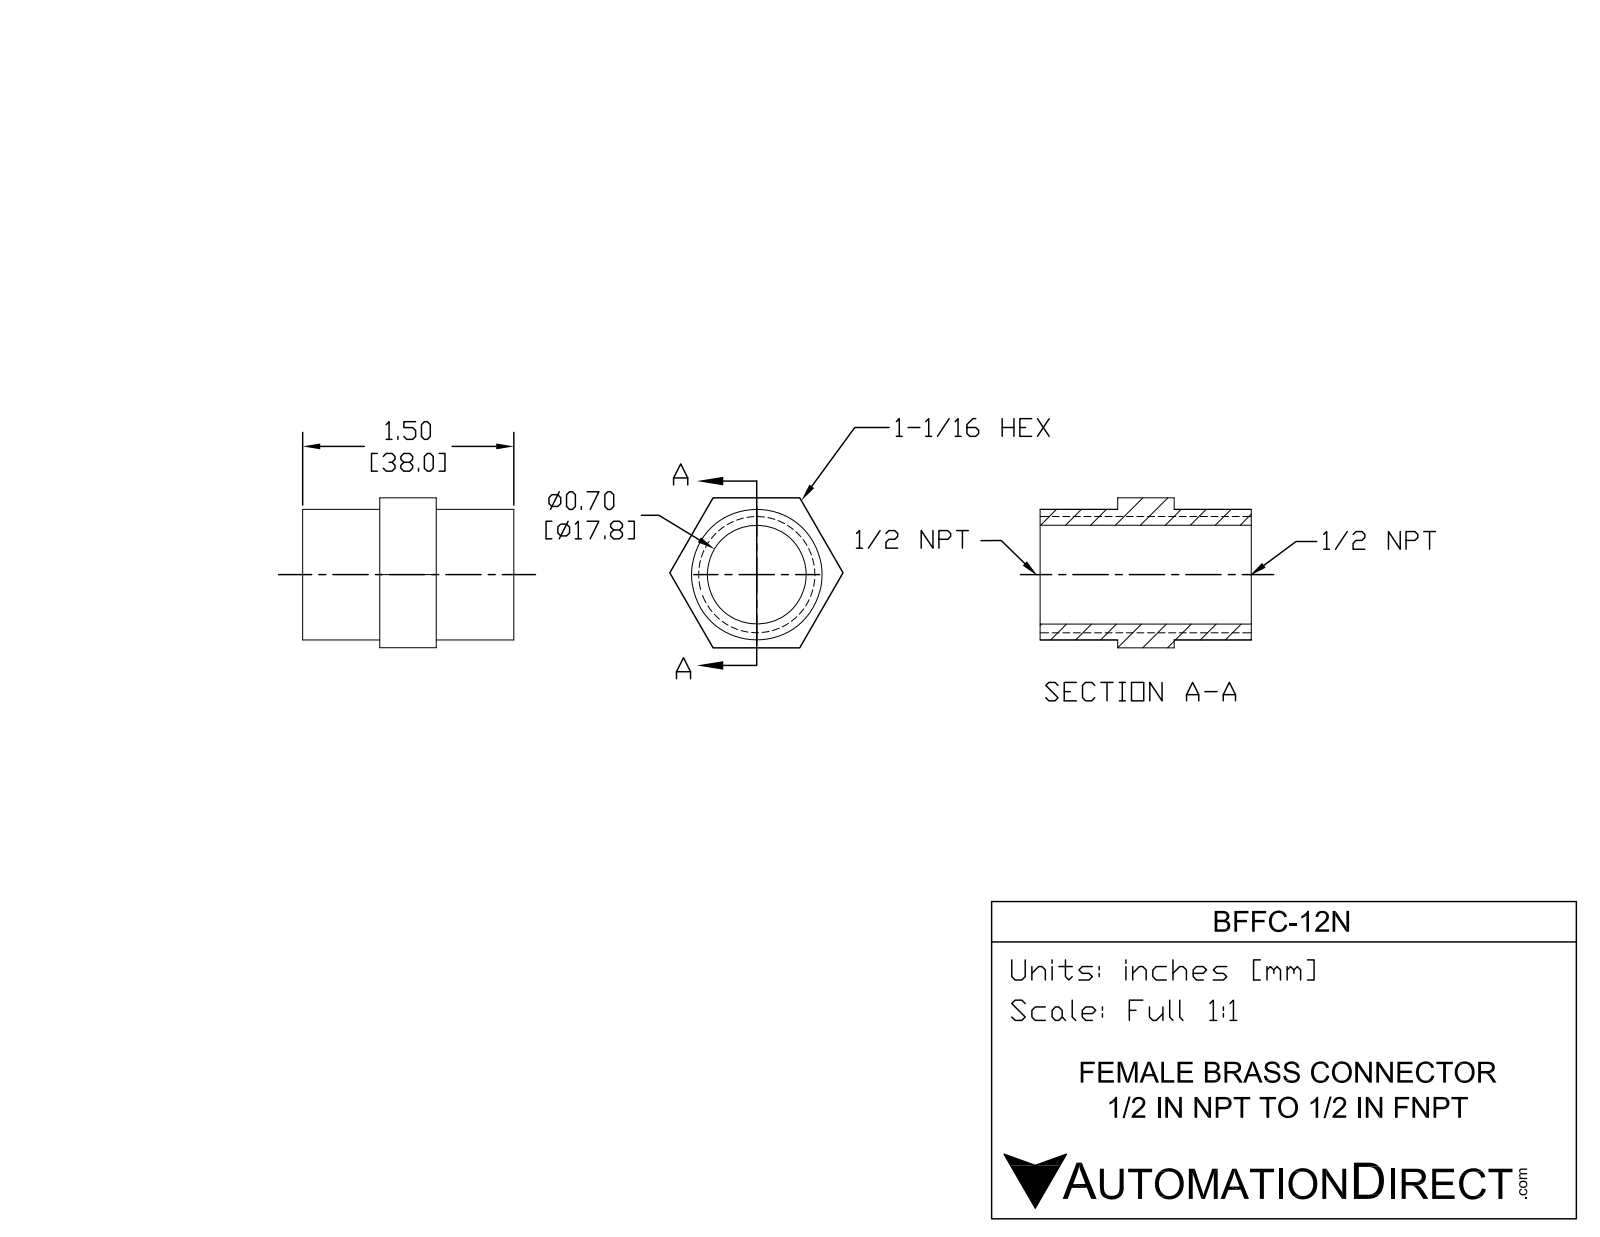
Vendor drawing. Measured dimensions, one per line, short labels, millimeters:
name: BFFC-12N
written by: SolidWorks 2015 (CONFIG_CONTROL_DESIGN)
unit: mm
bodies: 1 solid, 16 faces (10 planar, 6 cylindrical, 0 other)
size: 38 × 31.2 × 27
volume: 9 050 mm³; area: 5 892 mm²
holes: 1× ⌀17.8
bosses: 1× ⌀23.5
face distances: 27, 10.2, 13.9, 24, 38, 24.1, 14
